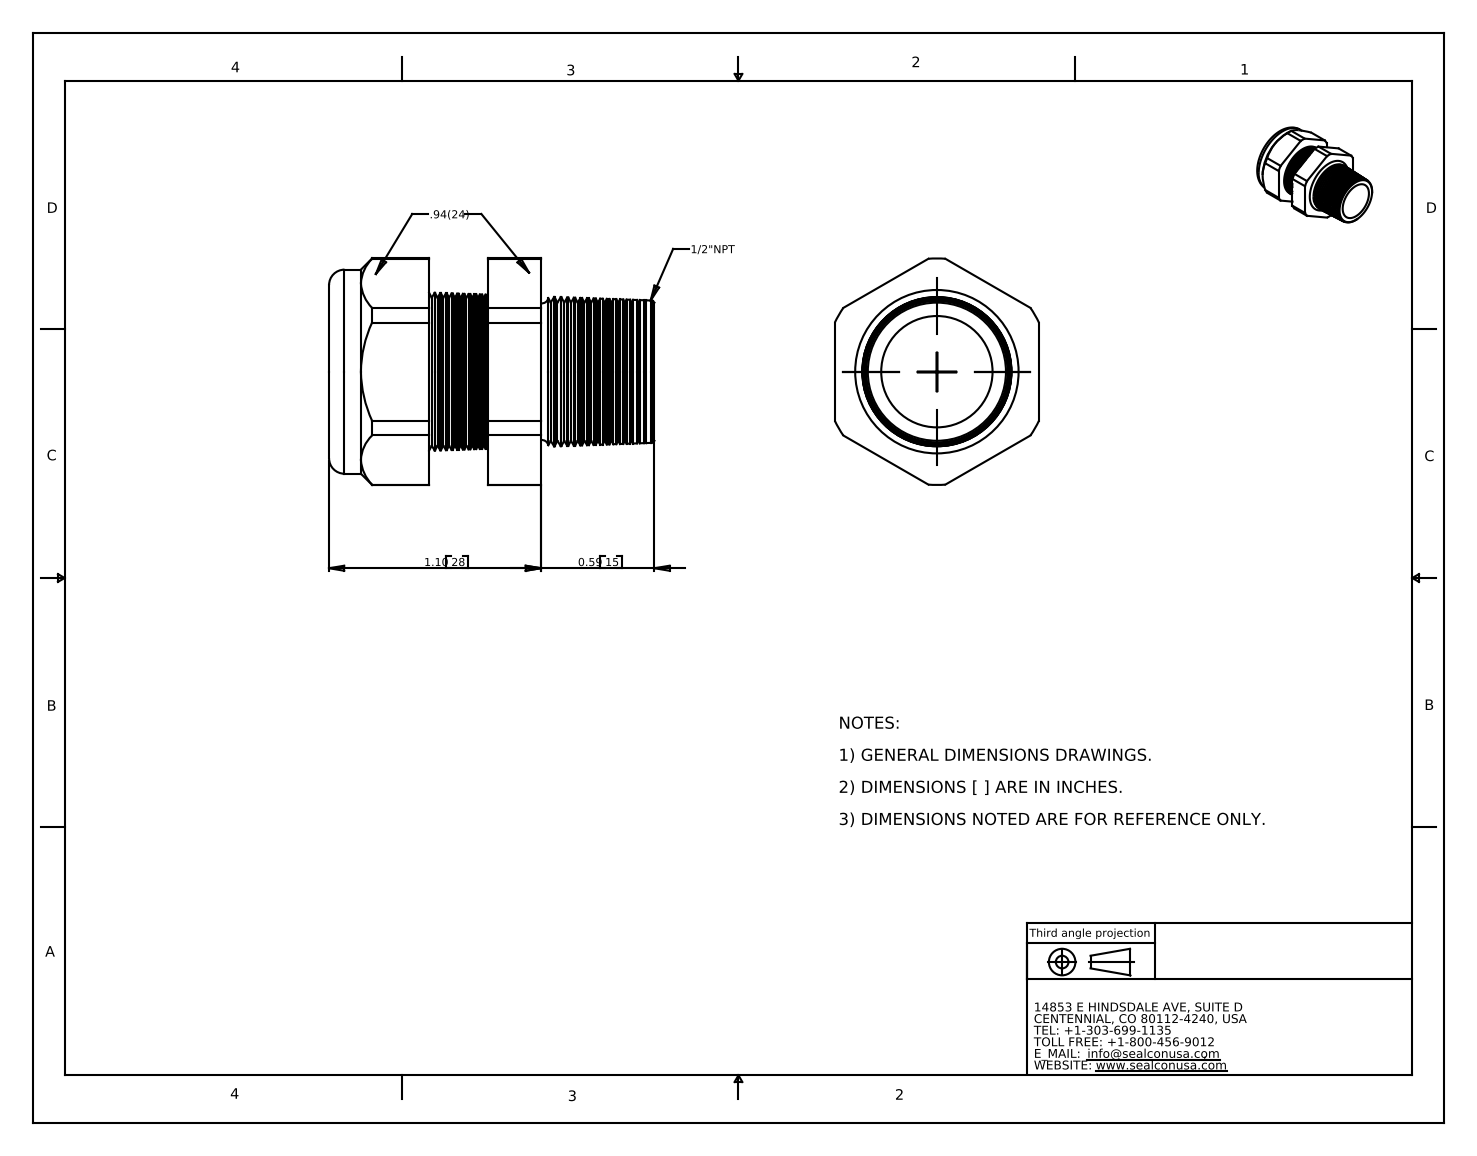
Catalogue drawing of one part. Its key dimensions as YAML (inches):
part_name: "CD16NP-BK"
step_written_by: "SolidWorks 2007 (CONFIG_CONTROL_DESIGN)"
units: inches
bodies: {solids: 2, faces: 210, planar: 20, cylindrical: 20, other: 170}
overall_size: [1.69, 1.177, 1.06]
volume: 0.778
surface_area: 13.01
round_holes:
  - {diameter: 0.58, count: 1}
  - {diameter: 0.6, count: 1}
round_bosses_or_shafts:
  - {diameter: 1.06, count: 1}
partial_cylinders:
  - {radius: 0.588, count: 1}
face_to_face_distances: [1.06, 0.305, 0.58, 0.276, 0.52, 0.824, 1.1, 0.35, 0.17, 0.474]
